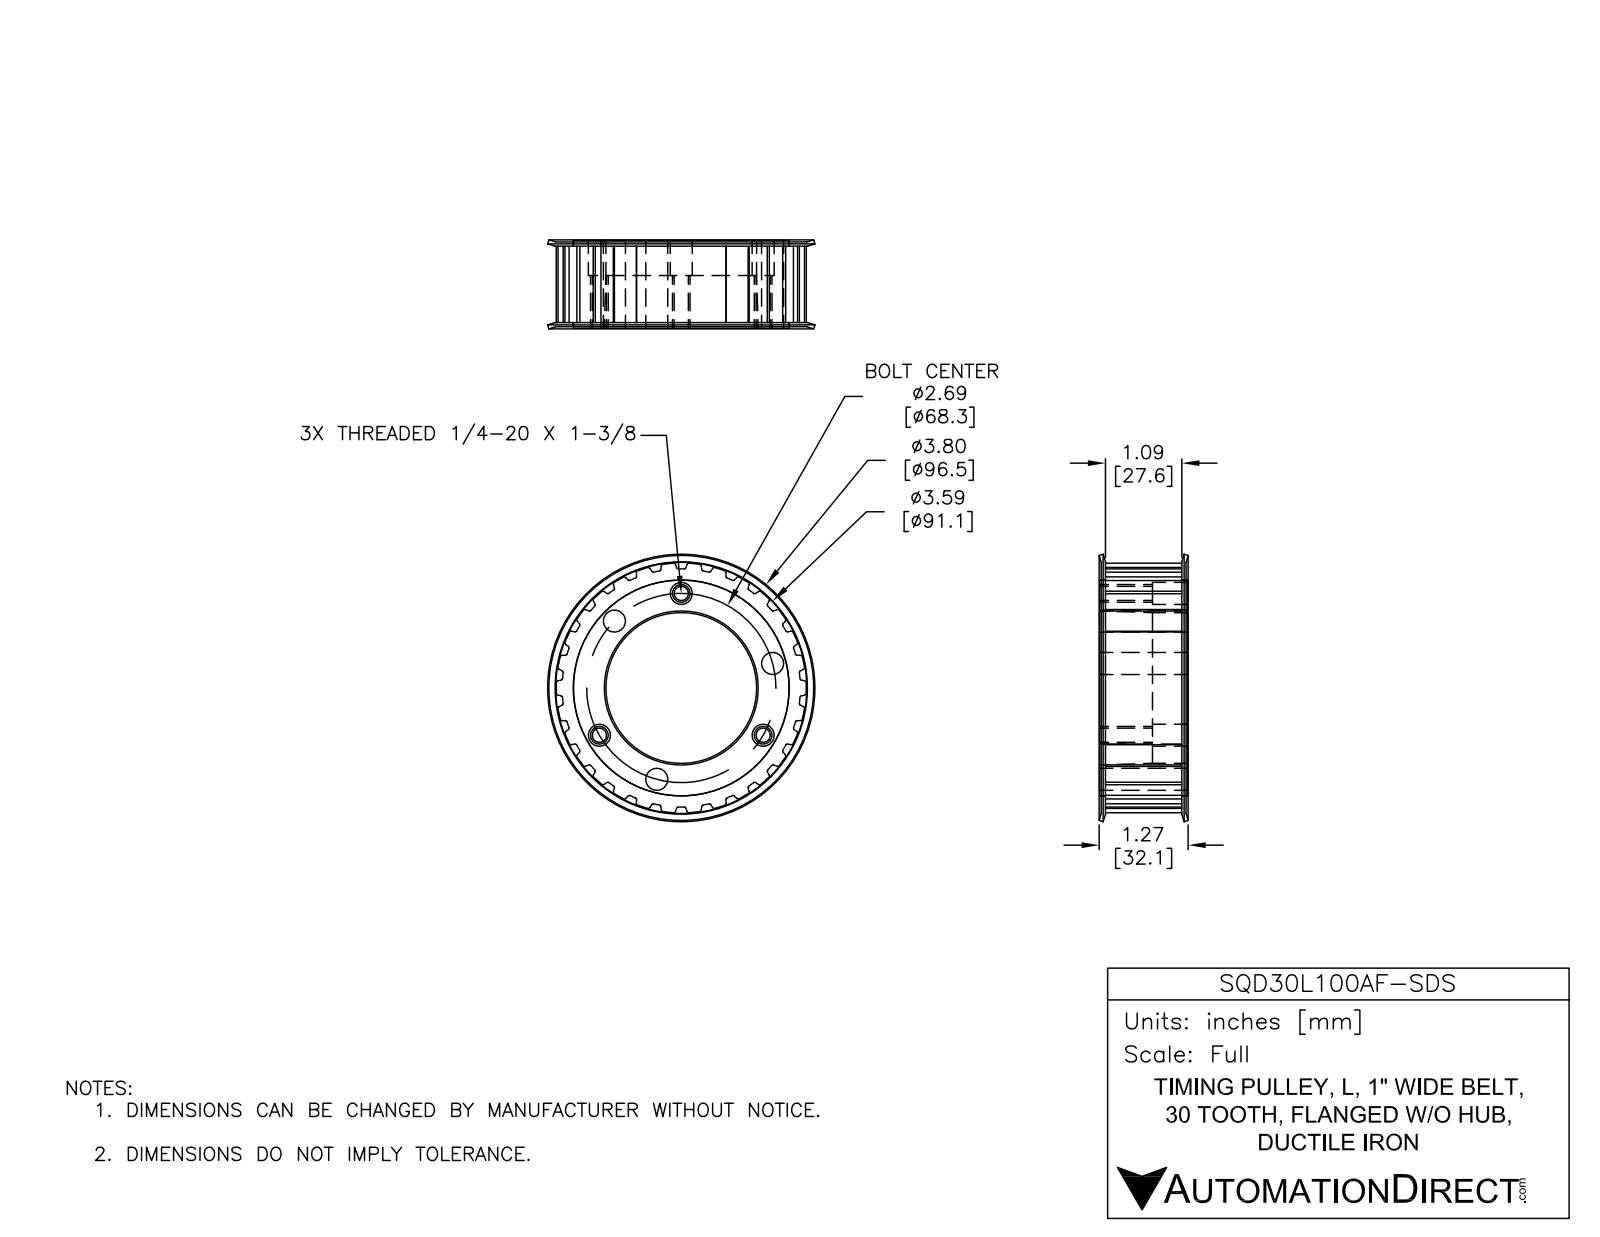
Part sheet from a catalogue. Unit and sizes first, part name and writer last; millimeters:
Units: millimetres
Overall size (bounding box): 96.5 × 96.5 × 32.1
Round holes (diameter × count): ⌀8 ×6, ⌀5.1 ×3, ⌀54.4 ×1, ⌀77.9 ×1
Round bosses / shafts (diameter × count): ⌀77.8 ×1
Partial cylindrical surfaces — rounded edges, fillets, slot ends (radius × count): R0.5 ×60, R0.8 ×60, R45.1 ×1
Main face-to-face distances: 31.8, 0.6, 31.2, 30.6, 31.2, 0.6, 1.5, 29.1, 2.1, 29.7
Hole centre spacings: 34.1, 59.1, 67.7, 26.1, 41.6, 26.1, 41.6, 59.1
Volume: 114 700 mm³ · Surface area: 33 860 mm²
Bodies: 1 solid, 318 faces (101 planar, 203 cylindrical, 14 other)
Part name (STEP PRODUCT): SQD30L100AF-SDS
STEP written by: SolidWorks 2018 (AUTOMOTIVE_DESIGN)
